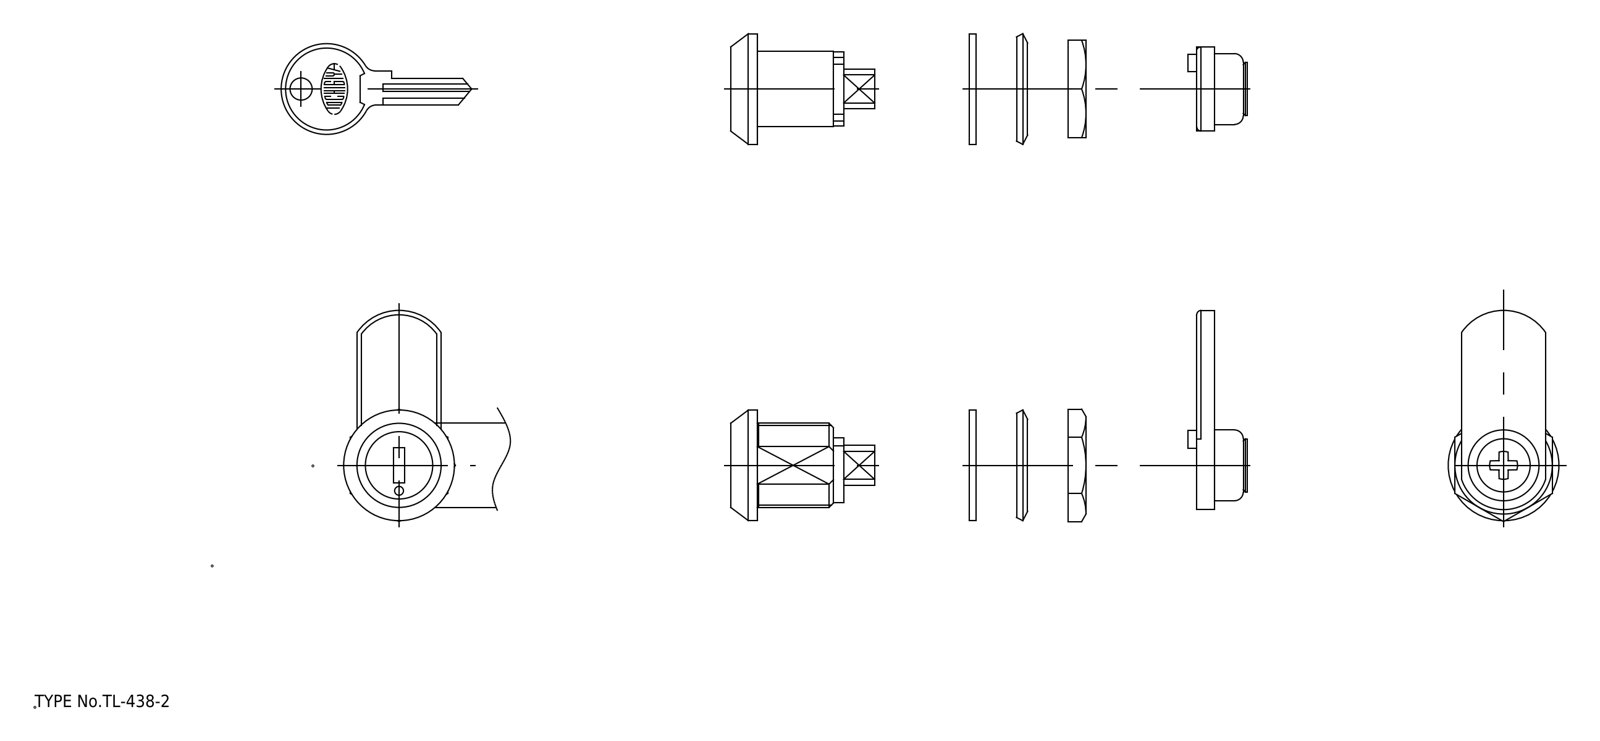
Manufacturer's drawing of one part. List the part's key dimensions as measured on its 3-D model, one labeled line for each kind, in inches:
Part name (STEP PRODUCT): 止め金具; TL_438_M1; TL_438_M2; TL_438_M4 (+5 more)
STEP written by: spGate 19.8.4 (****-****-****-****) (AUTOMOTIVE_DESIGN)
Units: inches
Bodies: 9 solids, 144 faces (66 planar, 55 cylindrical, 23 other)
Overall size (bounding box): 3.878 × 1.878 × 0.984
Volume: 0.834 in³ · Surface area: 17.48 in²
Round holes (diameter × count): ⌀0.197 ×1, ⌀0.236 ×1, ⌀0.472 ×1, ⌀0.496 ×1, ⌀0.61 ×1, ⌀0.748 ×1, ⌀0.787 ×1
Round bosses / shafts (diameter × count): ⌀0.984 ×1, ⌀0.807 ×1, ⌀0.602 ×1, ⌀0.492 ×1, ⌀0.157 ×1
Partial cylindrical surfaces — rounded edges, fillets, slot ends (radius × count): R0.039 ×2, R0.098 ×2, R0.124 ×1, R0.217 ×1, R0.226 ×1, R0.315 ×1, R0.331 ×1, R0.453 ×1
Main face-to-face distances: 0.157, 0.768, 0.071, 0.925, 0.059, 0.709, 0.866, 0.669, 0.236, 0.299
